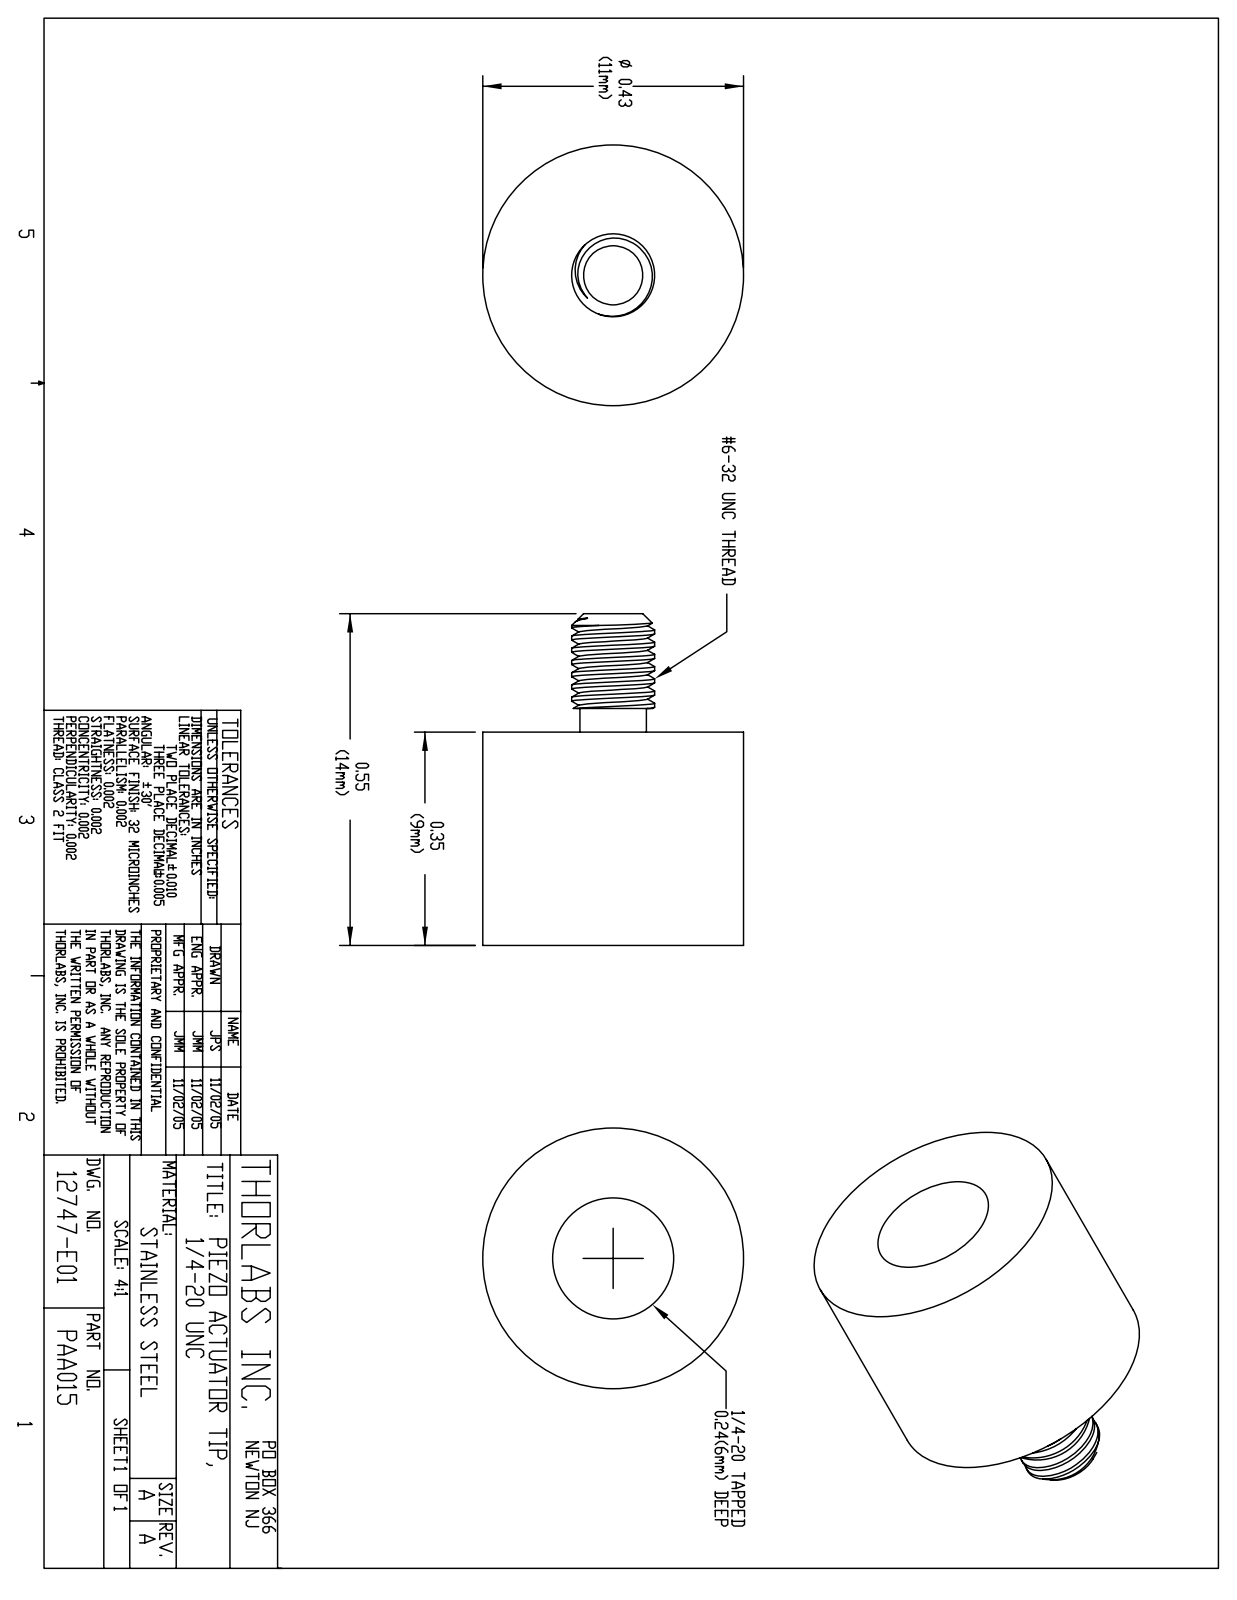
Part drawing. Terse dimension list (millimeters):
name: 12747-E0W
written by: SolidWorks 2007 (AUTOMOTIVE_DESIGN)
unit: mm
bodies: 0 solids, 28 faces (3 planar, 21 cylindrical, 4 other)
size: 14 × 11 × 11
holes: 1× ⌀5.1
bosses: 1× ⌀11, 1× ⌀3.5, 1× ⌀2.8
face distances: 9, 14, 5
